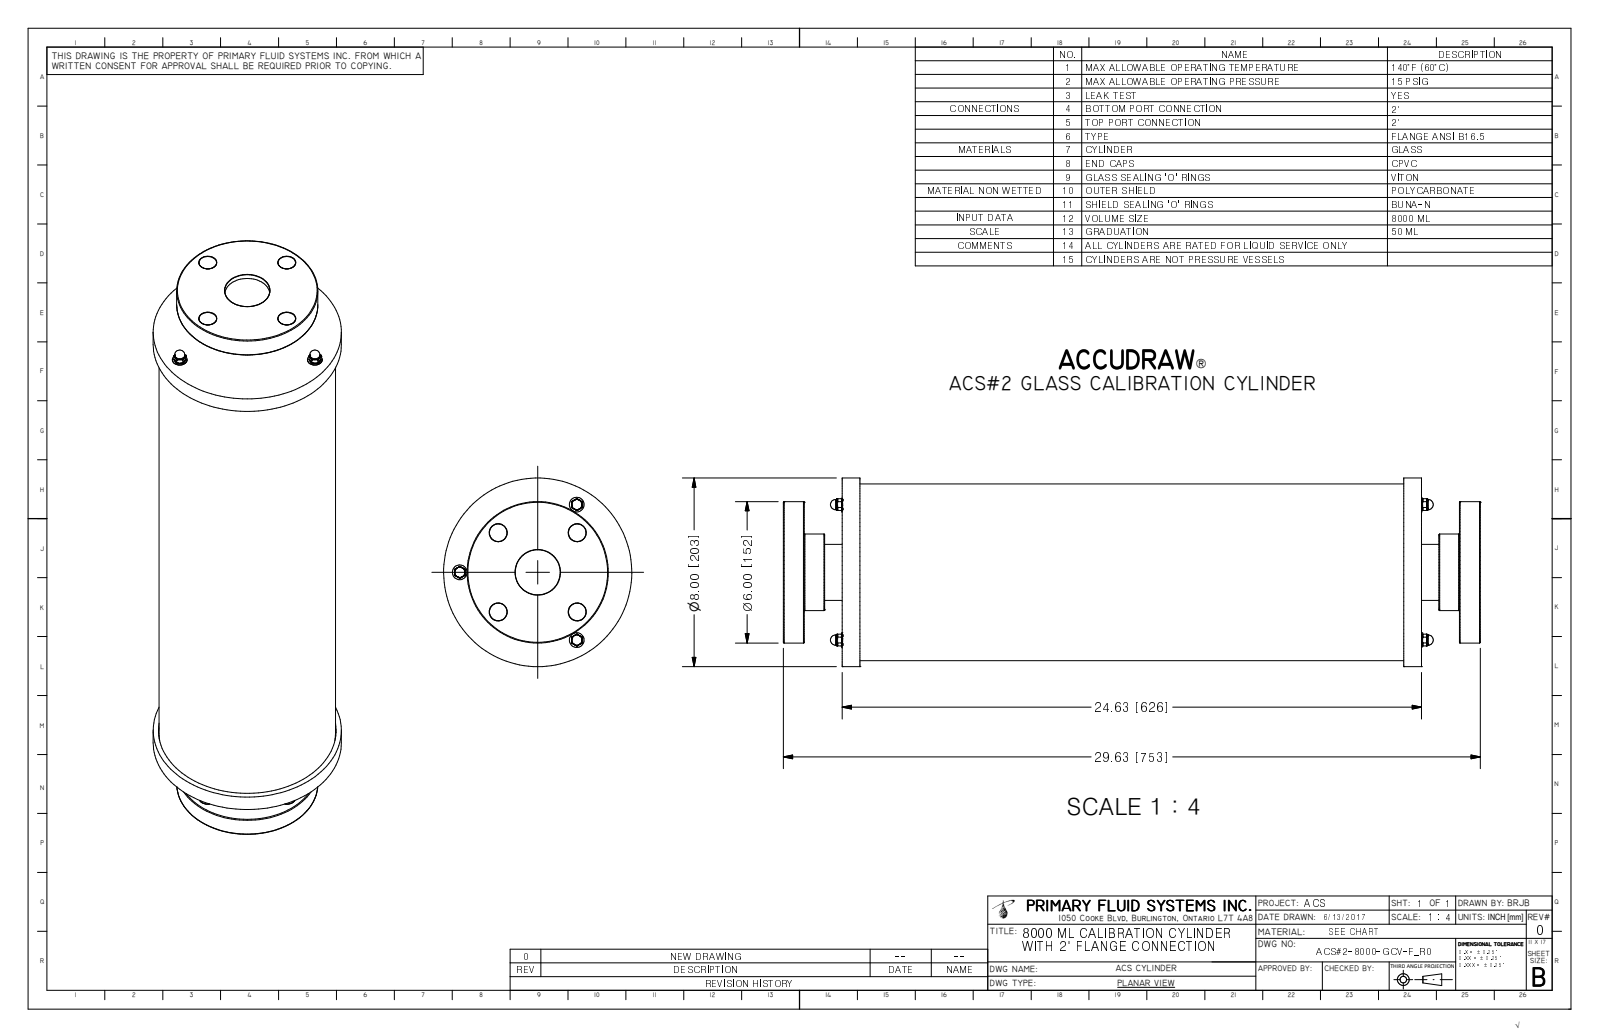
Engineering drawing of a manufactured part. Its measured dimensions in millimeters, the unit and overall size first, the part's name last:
Units: millimetres
Overall size (bounding box): 752.6 × 203.2 × 203.2
Round holes (diameter × count): ⌀18.9 ×4, ⌀48.6 ×1, ⌀49.3 ×1
Round bosses / shafts (diameter × count): ⌀15.9 ×3, ⌀203.2 ×1, ⌀190.5 ×1, ⌀152.4 ×1, ⌀82.4 ×1, ⌀60.3 ×1
Main face-to-face distances: 63.5, 689.1, 625.6, 22.5, 730.1, 41, 666.6, 752.6, 707.6, 606.6
Hole centre spacings: 60.3, 85.3, 120.7
Volume: 18 830 000 mm³ · Surface area: 607 100 mm²
Bodies: 1 solid, 201 faces (22 planar, 27 cylindrical, 152 other)
Part name (STEP PRODUCT): ACS#2-8000-GCV-F_R0
STEP written by: Autodesk Inventor 2009 (AUTOMOTIVE_DESIGN)
